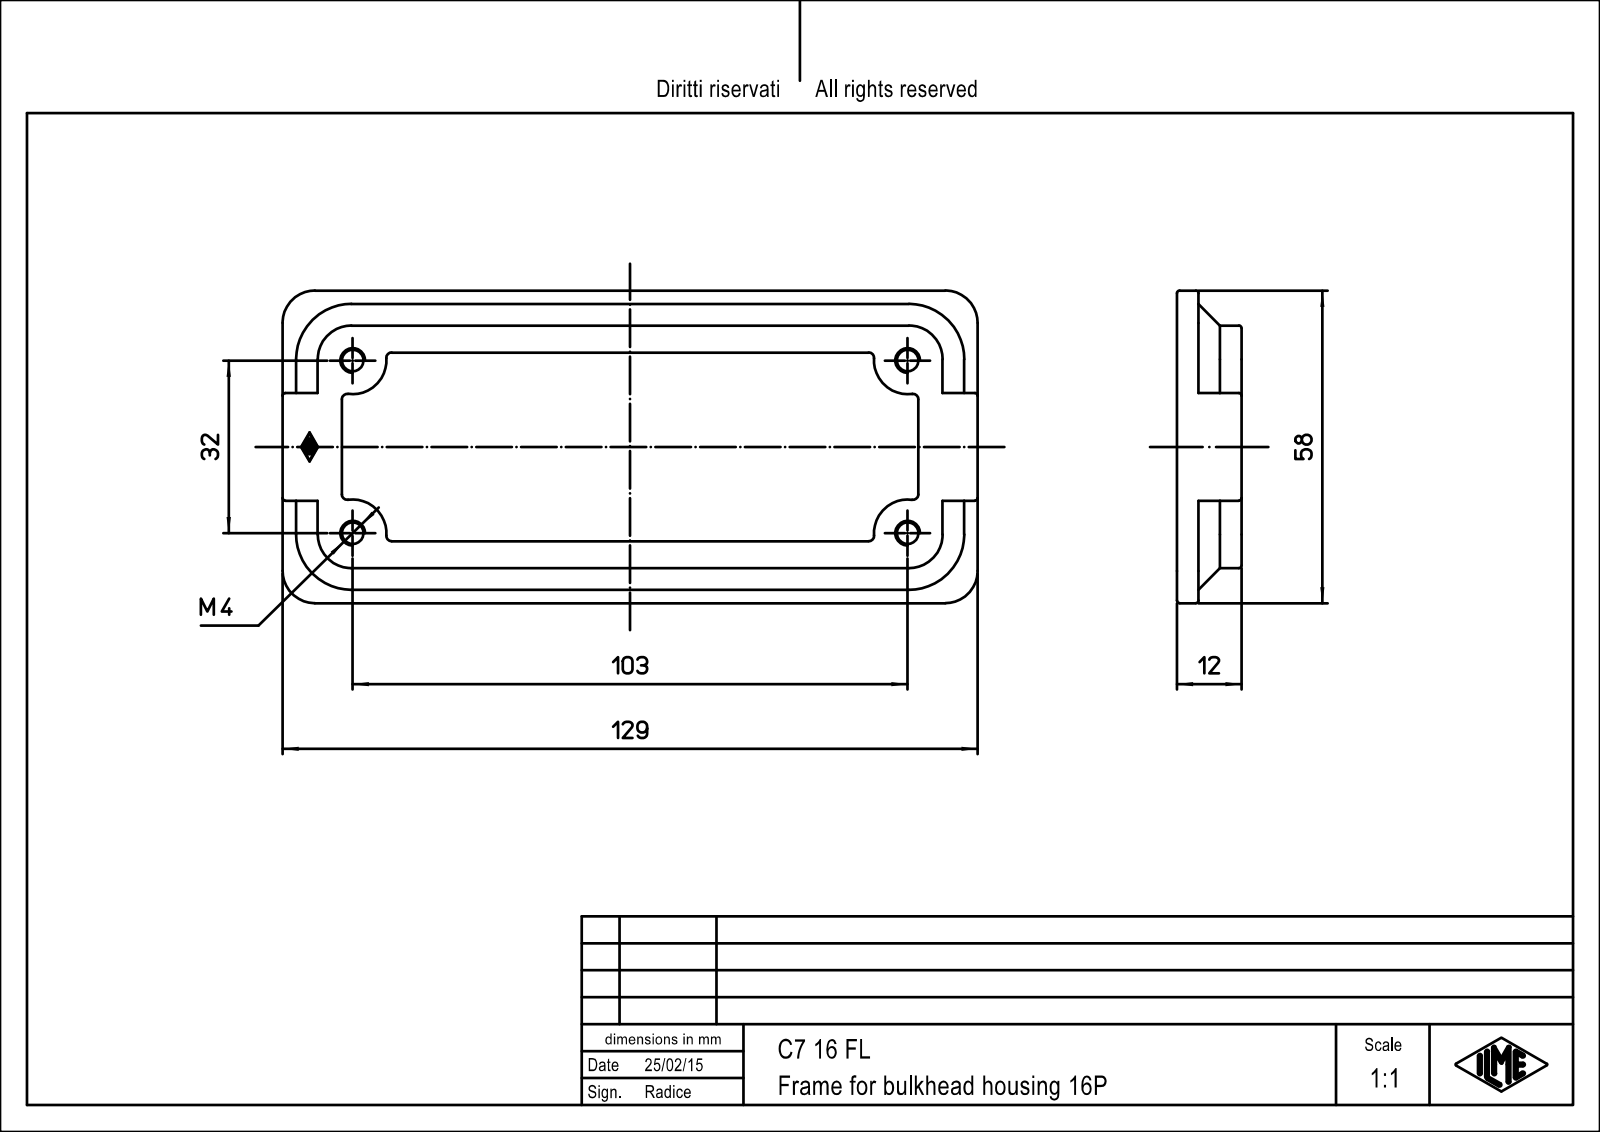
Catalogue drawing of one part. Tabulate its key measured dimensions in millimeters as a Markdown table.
| quantity | value |
| --- | --- |
| part name | C7_16_FL |
| STEP written by | Creo Elements/Direct Modeling 18.1F 24-Jul-2014 (C) Parametric Technology GmbH (AUTOMOTIVE_DESIGN) |
| units | millimeters |
| bodies | 1 solid, 169 faces (65 planar, 72 cylindrical, 32 other) |
| overall size | 129 × 58 × 12 |
| volume | 32 680 mm³ |
| surface area | 14 835 mm² |
| round holes (diameter × count) | 4 × 4 |
| partial cylindrical surfaces (radius × count) | 0.5 × 24, 0.1 × 14, 1 × 8, 6.25 × 8, 6 × 4 |
| main face-to-face distances | 12, 35, 6.5, 5, 40, 4, 8, 11.5, 46.5, 51.5 |
| hole center spacings | 32, 103, 107.86 |
